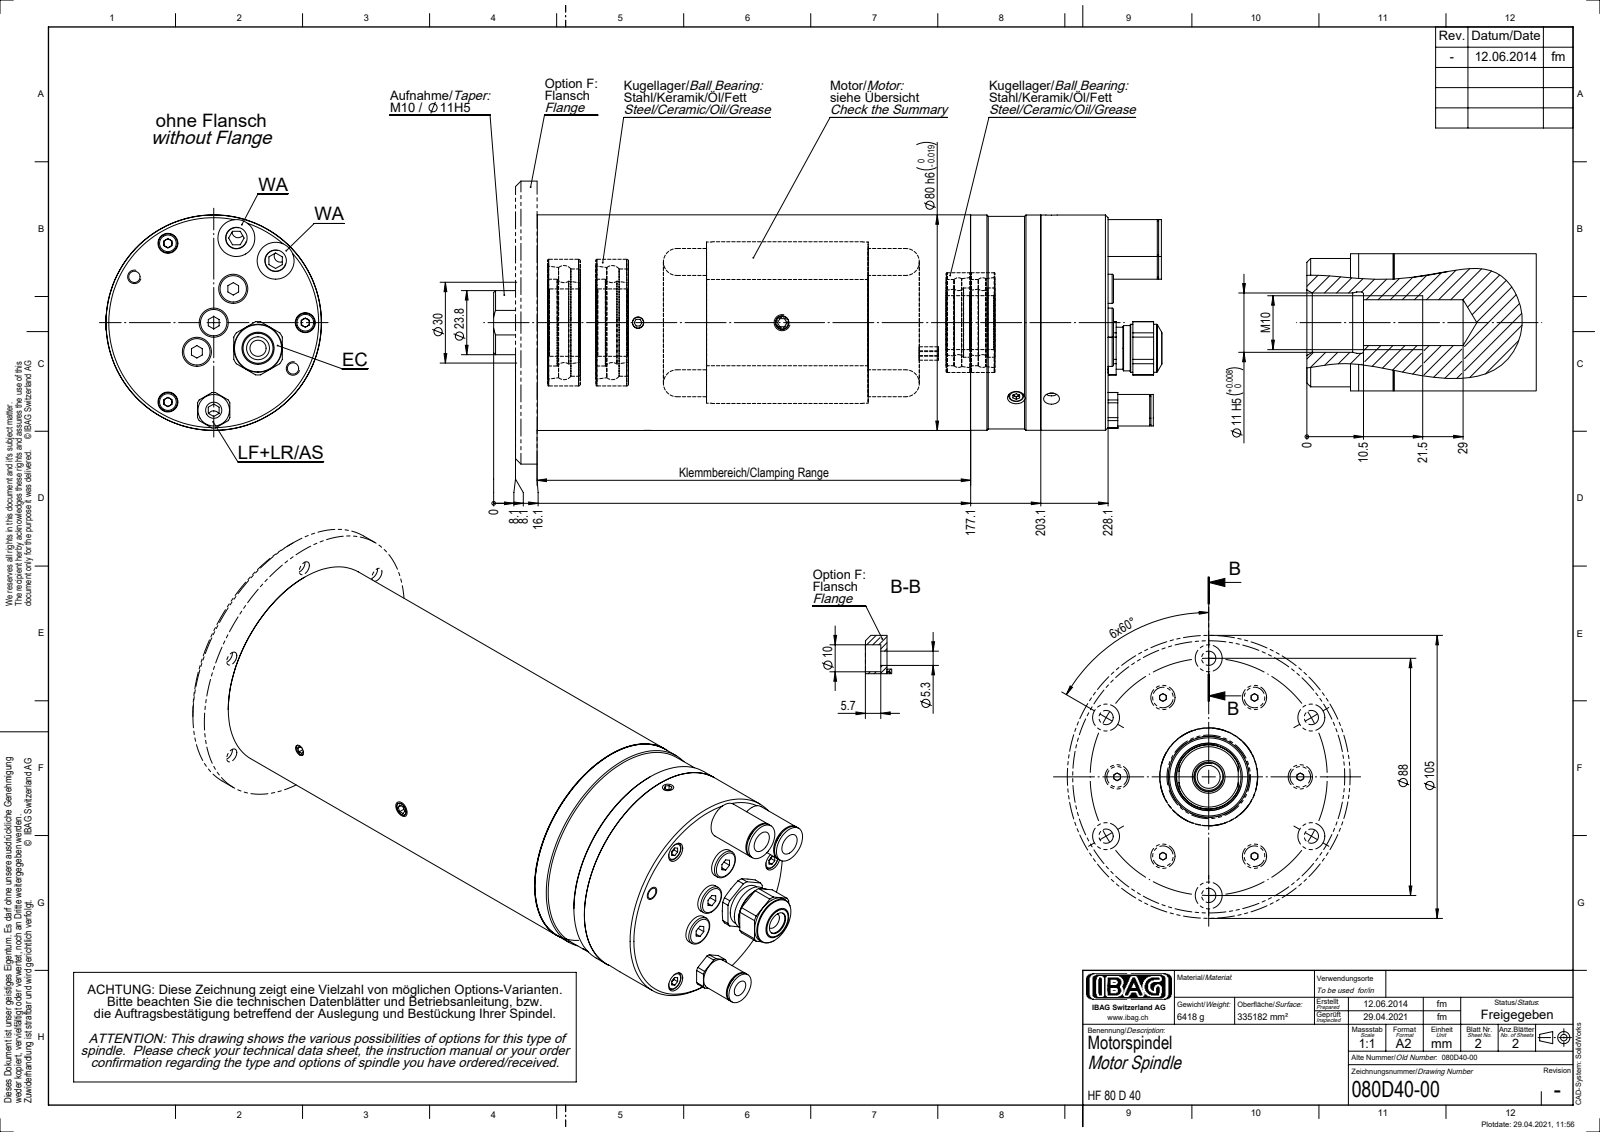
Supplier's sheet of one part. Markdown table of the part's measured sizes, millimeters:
| quantity | value |
| --- | --- |
| part name | 080D40-00 |
| STEP written by | SolidWorks 2014 (CONFIG_CONTROL_DESIGN) |
| units | millimeters |
| bodies | 0 solids, 367 faces (160 planar, 121 cylindrical, 86 other) |
| overall size | 250.1 × 80 × 80 |
| round holes (diameter × count) | 7.4 × 3, 8 × 3, 4.2 × 2, 1.5 × 1, 3.3 × 1, 5.9 × 1, 6 × 1, 6.5 × 1, 10.7 × 1, 11 × 1, 16.2 × 1, 24 × 1 |
| round bosses / shafts (diameter × count) | 7.64 × 6, 14 × 2, 13.7 × 2, 13.7 × 2, 13 × 2, 80 × 1, 79.9 × 1, 79.8 × 1 |
| partial cylindrical surfaces (radius × count) | 6.6 × 1, 9.9 × 1, 11.9 × 1 |
| main face-to-face distances | 25, 195, 220, 8, 187, 212, 51, 169, 161, 26 |
| hole center spacings | 34, 32.5, 40.5, 48.08, 52.76, 58.89, 65.68, 13.1 |
